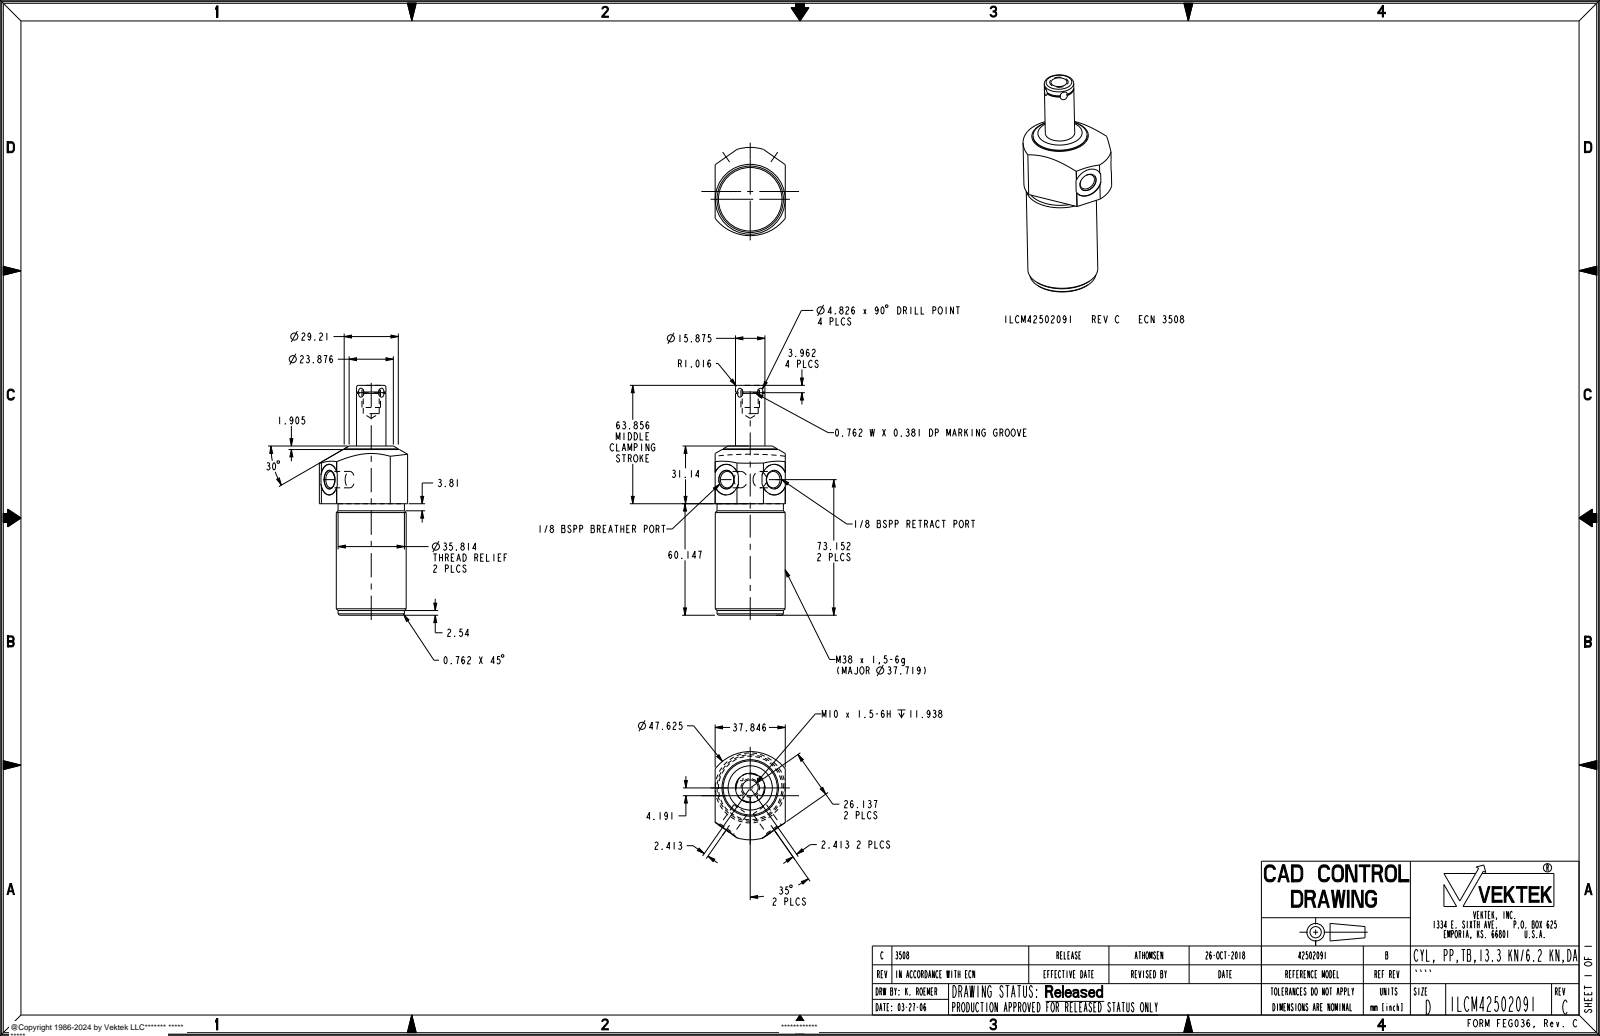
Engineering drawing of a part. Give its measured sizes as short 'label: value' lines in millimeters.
name: ILCM42502091
written by: PRO/ENGINEER BY PARAMETRIC TECHNOLOGY CORPORATION, 2013320 (AUTOMOTIVE_DESIGN)
unit: mm
bodies: 1 solid, 88 faces (24 planar, 38 cylindrical, 26 other)
size: 124 × 47.62 × 37.85
volume: 114 738 mm³; area: 17 298 mm²
holes: 2× ⌀8.84, 2× ⌀10.03, 1× ⌀8.61
bosses: 1× ⌀37.72, 1× ⌀35.81, 1× ⌀29.21, 1× ⌀15.88, 1× ⌀10.01
rounds: 2× R8.26, 1× R7.56, 1× R23.81
face distances: 37.84, 60.15, 91.29, 31.14, 13.46, 124.01, 63.86, 32.72, 13.72, 13.71
